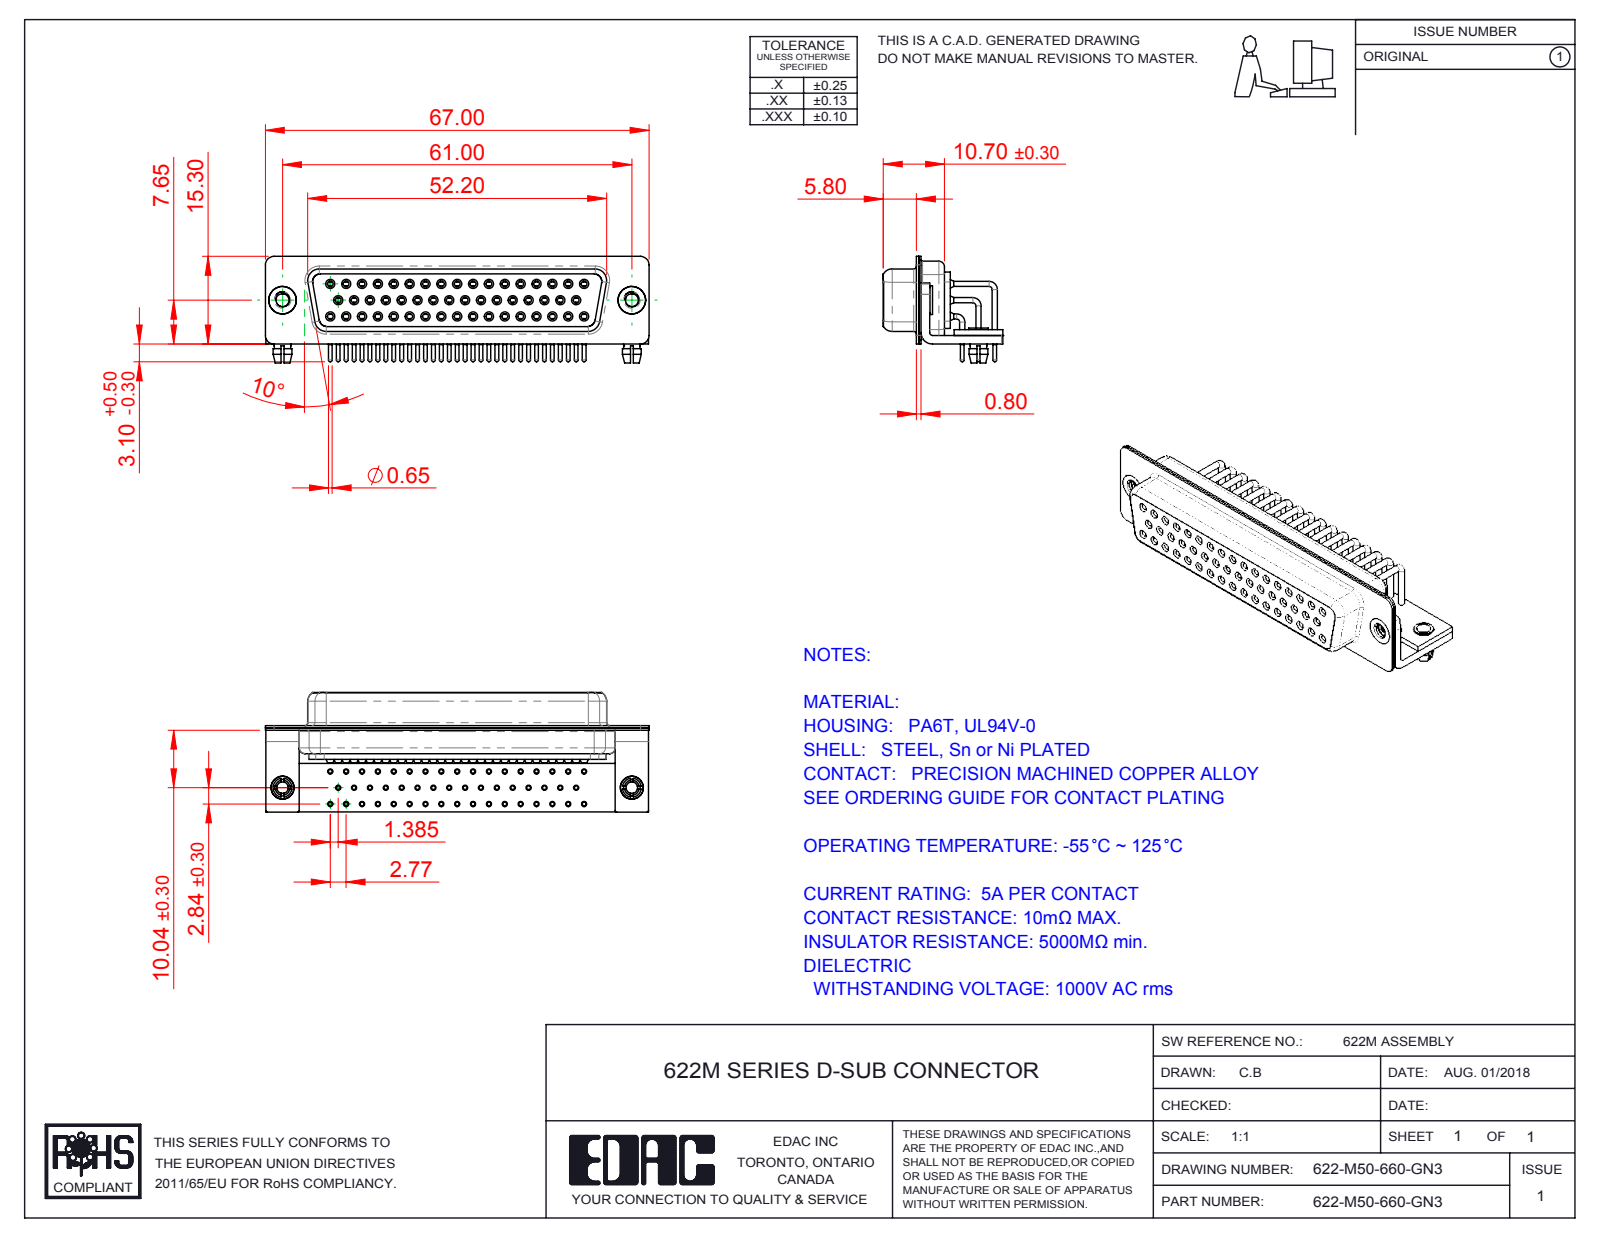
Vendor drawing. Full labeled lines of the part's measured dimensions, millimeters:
Part name (STEP PRODUCT): 622M Contact Row 3; 622M Contact Row 1_50 Contacts; 622M Contact Row 2_50 Contacts; 622M Board Lock_50 Contacts (+7 more)
STEP written by: SolidWorks 2016 (CONFIG_CONTROL_DESIGN)
Units: millimetres
Bodies: 60 solids, 3171 faces (891 planar, 1441 cylindrical, 839 other)
Overall size (bounding box): 67 × 20.9 × 18.6
Volume: 7 790 mm³ · Surface area: 18 357 mm²
Round holes (diameter × count): ⌀2 ×52, ⌀0.9 ×50, ⌀1 ×50, ⌀1.1 ×50, ⌀1.7 ×50, ⌀1.8 ×50, ⌀2.26 ×2, ⌀2.5 ×2, ⌀3.2 ×2, ⌀4 ×2, ⌀4.8 ×2
Round bosses / shafts (diameter × count): ⌀0.9 ×59, ⌀1.6 ×50, ⌀1.5 ×50, ⌀0.65 ×50, ⌀5 ×2, ⌀4.9 ×2, ⌀4 ×2, ⌀3.4 ×2
Partial cylindrical surfaces — rounded edges, fillets, slot ends (radius × count): R0.25 ×16, R1.5 ×16, R2 ×13, R1.35 ×8, R1.6 ×8, R0.5 ×5, R0.6 ×4, R0.65 ×4
Main face-to-face distances: 0.4, 1, 2.2, 0.85, 1.35, 11.85, 12.25, 5.8, 5.9, 0.8
Hole centre spacings: 2.77, 3.16, 5.54, 8.31, 11.08, 13.85, 16.62, 19.39
